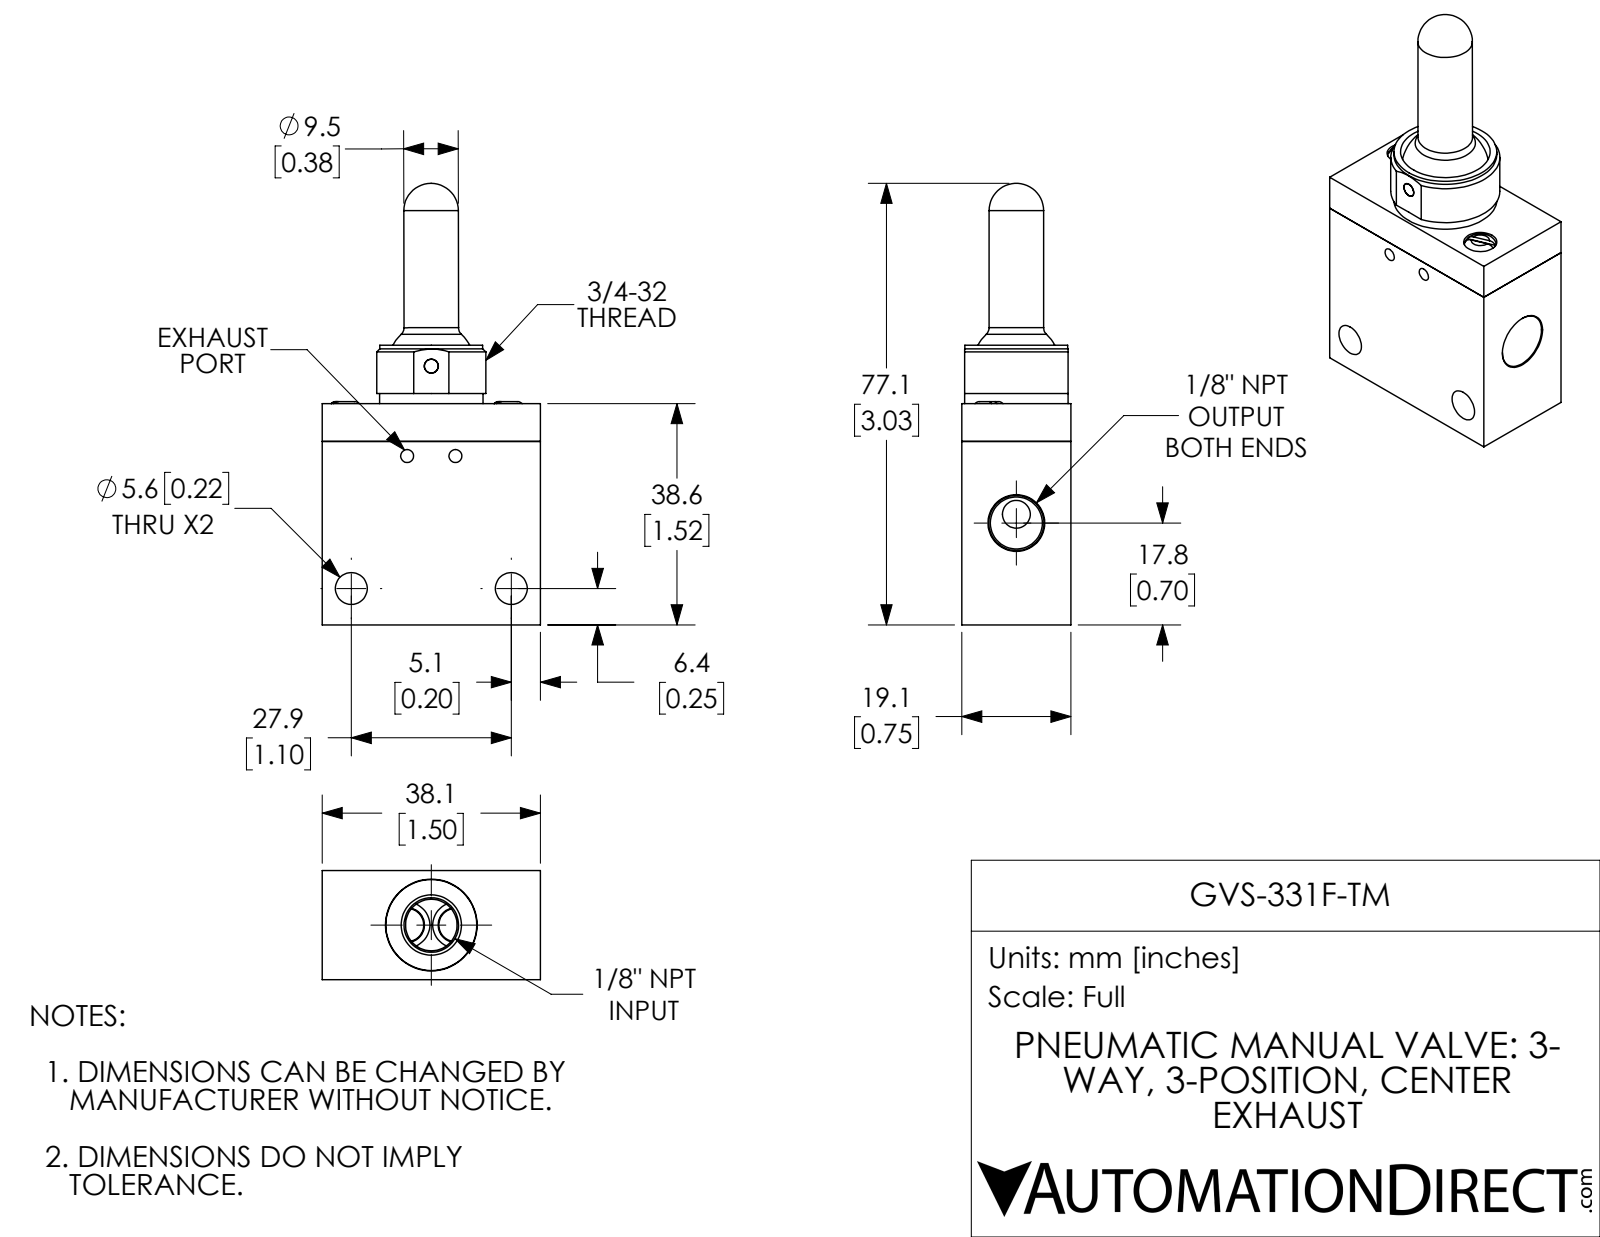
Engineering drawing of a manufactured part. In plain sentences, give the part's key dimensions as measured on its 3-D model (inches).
The part is named "GVS-331F-TM". Its 3-D file was written by "SolidWorks 2018 (AUTOMOTIVE_DESIGN)". It is 7 solids with 160 faces: 46 planar, 74 cylindrical and 40 other. Overall it measures 3.034 by 1.5 by 0.75 inches. Its volume is 1.499 cubic inches and its surface area 21.95 square inches. Round holes: 4 of diameter 0.228, 2 of diameter 0.089, 2 of diameter 0.098, 2 of diameter 0.129, 2 of diameter 0.219, 2 of diameter 0.312, 1 of diameter 0.096, 1 of diameter 0.097, 1 of diameter 0.191, 1 of diameter 0.57, 1 of diameter 0.616, 1 of diameter 0.625. Round bosses or shafts: 2 of diameter 0.22, 2 of diameter 0.118, 1 of diameter 0.71, 1 of diameter 0.707, 1 of diameter 0.63, 1 of diameter 0.375, 1 of diameter 0.1, 1 of diameter 0.095. Partial cylindrical surfaces (rounded edges, fillets, slot ends): 1 of radius 0.375. The main face-to-face distances are 0.75, 1.5, 1.26, 1.52, 0.26, 0.315, 0.945, 1.205, 0.02, 1.522. The hole center spacings are 0.166, 0.332, 0.64, 0.987, 1.158, 1.624, 0.408, 0.465.
